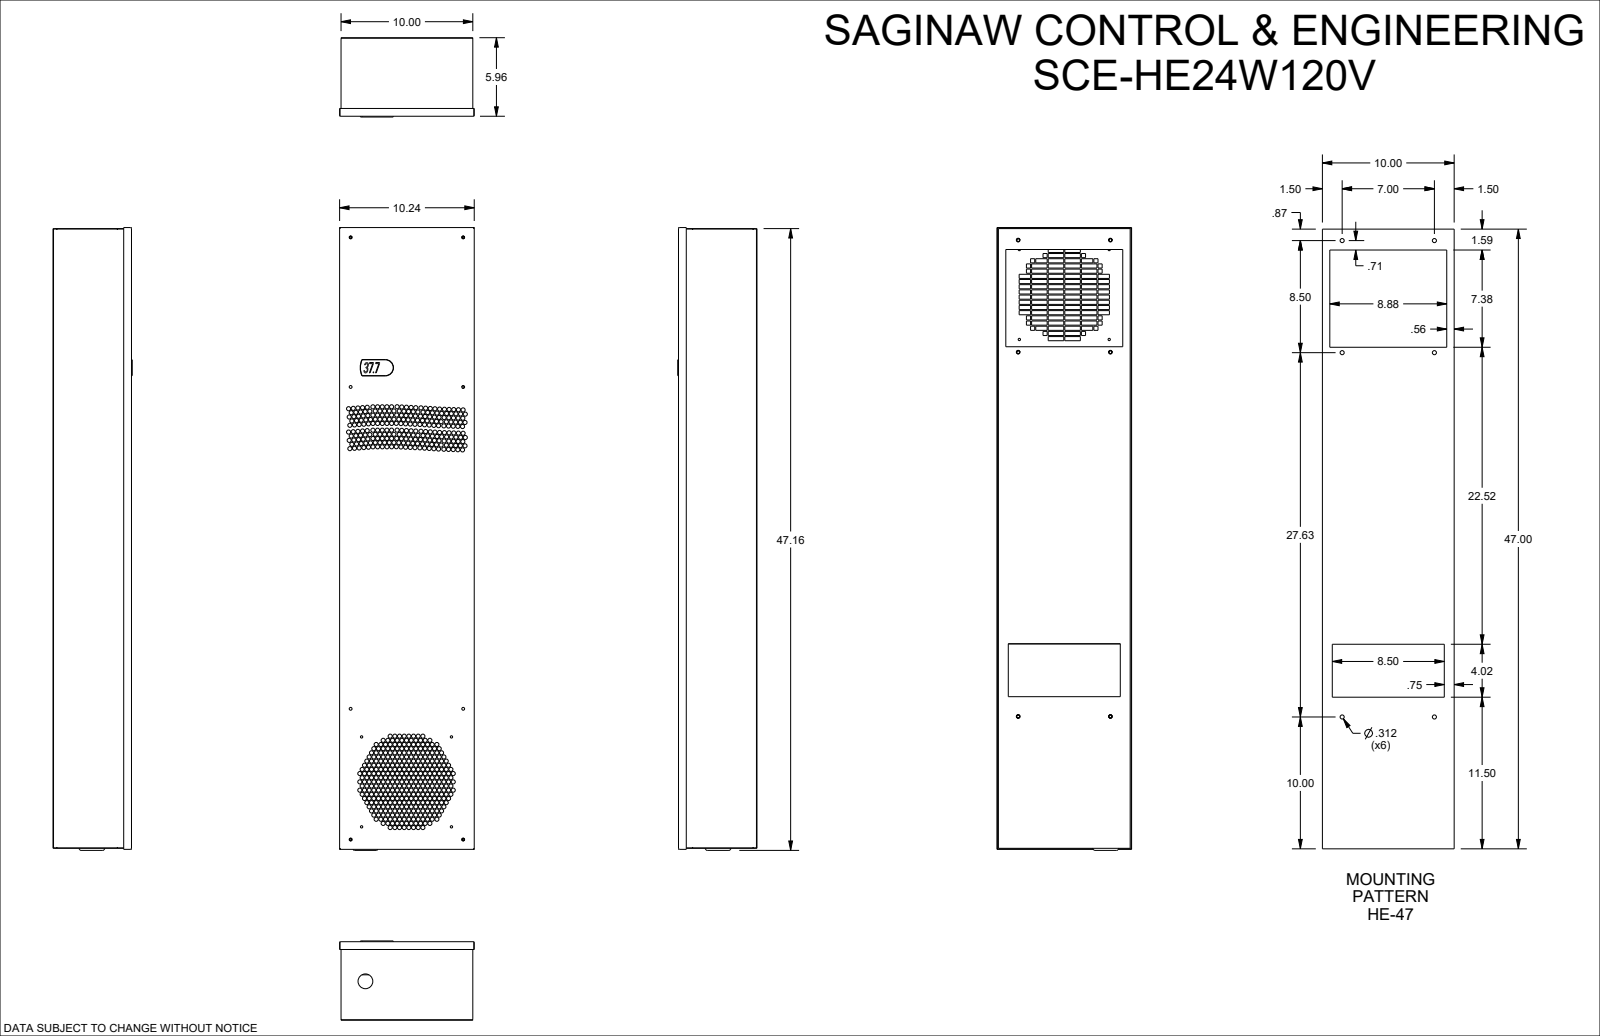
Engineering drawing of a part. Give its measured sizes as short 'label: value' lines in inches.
name: SCE-HE24W120V
written by: SolidWorks 2023 (AUTOMOTIVE_DESIGN)
unit: in
bodies: 1 solid, 1827 faces (1163 planar, 664 cylindrical, 0 other)
size: 47.157 × 10.217 × 6.085
volume: 2 801 in³; area: 1 668 in²
holes: 629× ⌀0.315, 8× ⌀0.177, 8× ⌀0.217, 6× ⌀0.276, 1× ⌀0.65
rounds: 8× R0.063, 1× R0.6, 1× R0.62, 1× R1.477, 1× R1.497
face distances: 5.957, 10, 0.031, 5.925, 5.894, 47, 0.108, 10.108, 0.063, 5.862
hole spacings: 0.723, 1.309, 0.948, 0.63, 0.354, 1.923, 1.446, 1.26
